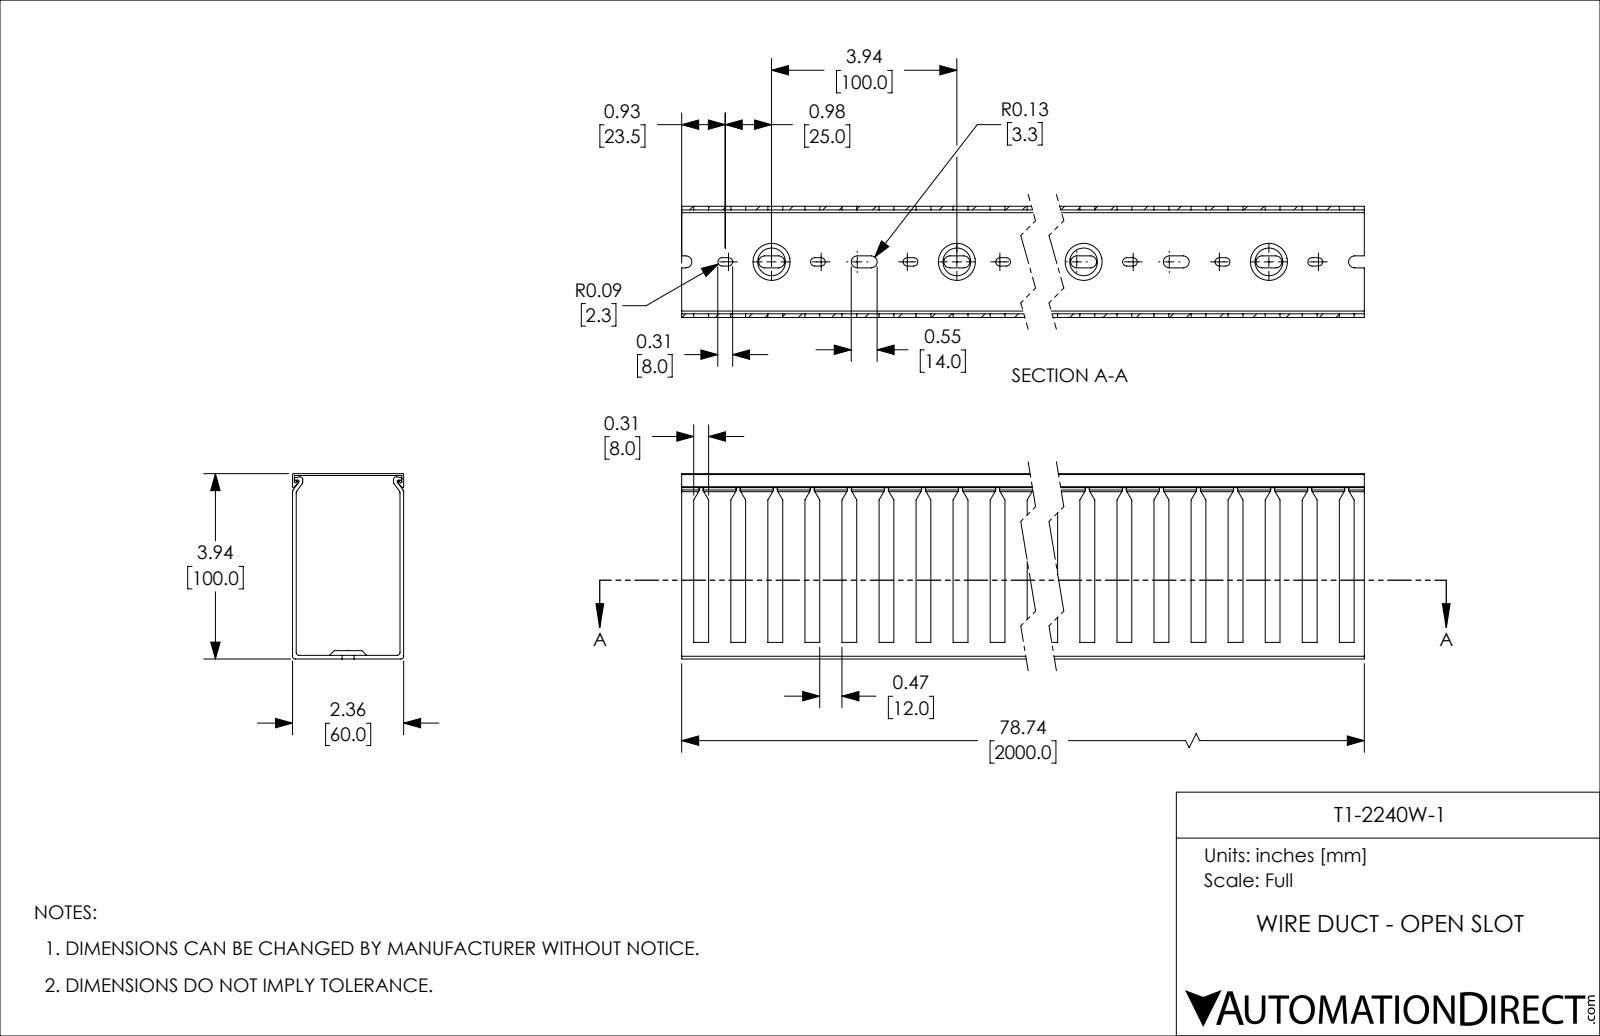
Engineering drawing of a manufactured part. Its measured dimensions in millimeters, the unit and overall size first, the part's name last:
Units: millimetres
Overall size (bounding box): 2000 × 100 × 60
Partial cylindrical surfaces — rounded edges, fillets, slot ends (radius × count): R2.25 ×80, R3.25 ×80, R1.5 ×12, R0.5 ×8, R0.75 ×6
Main face-to-face distances: 2, 58, 60, 56, 1, 100, 99, 97, 98, 59
Volume: 1 162 000 mm³ · Surface area: 1 322 000 mm²
Bodies: 2 solids, 1005 faces (534 planar, 431 cylindrical, 40 other)
Part name (STEP PRODUCT): T1-2240W-1
STEP written by: SolidWorks 2021 (CONFIG_CONTROL_DESIGN)
